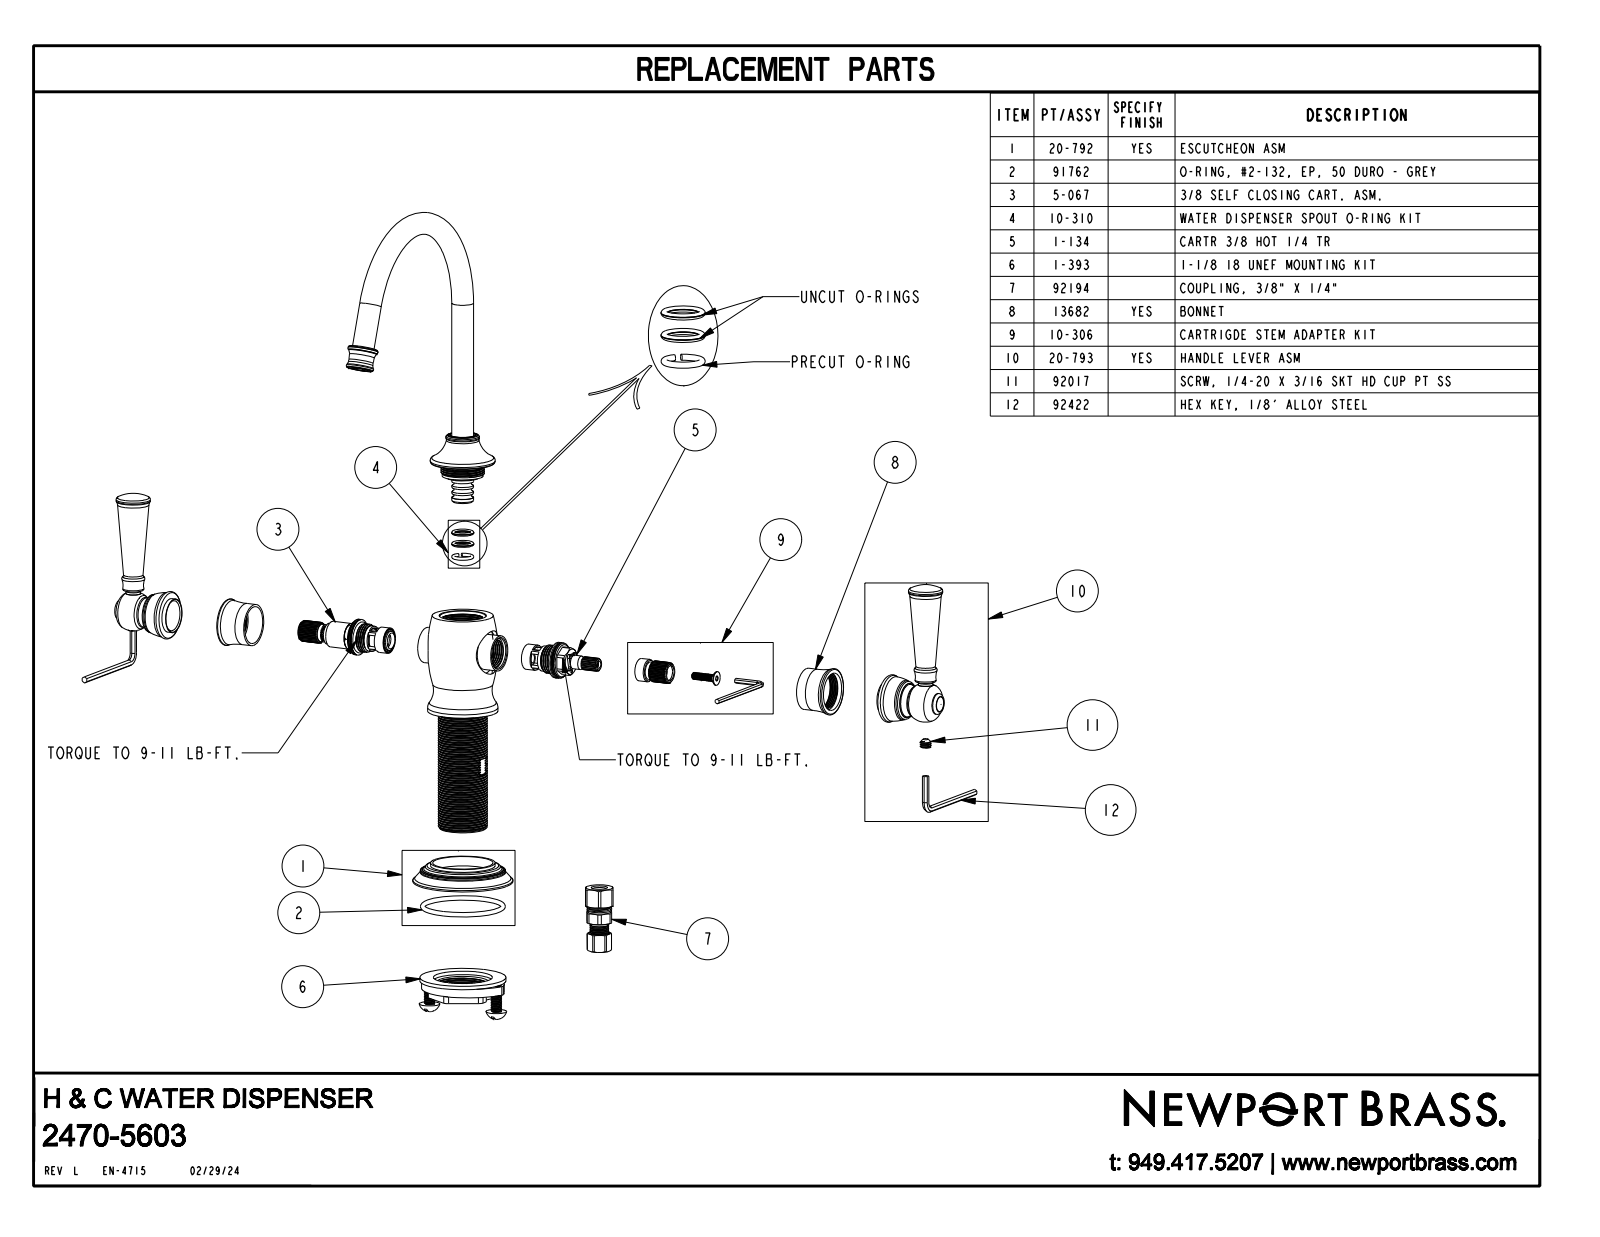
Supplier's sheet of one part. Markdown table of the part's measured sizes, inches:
| quantity | value |
| --- | --- |
| part name | 2470-5603 |
| STEP written by | CREO PARAMETRIC BY PTC INC, 2018400 (CONFIG_CONTROL_DESIGN) |
| units | inches |
| bodies | 1 solid, 243 faces (23 planar, 34 cylindrical, 186 other) |
| overall size | 9.456 × 6.18 × 5.353 |
| volume | 11.61 in³ |
| surface area | 62.91 in² |
| round holes (diameter × count) | 1 × 1 |
| round bosses / shafts (diameter × count) | 0.5 × 3, 0.785 × 2, 0.335 × 2, 0.33 × 2, 1.61 × 1, 0.95 × 1, 0.48 × 1 |
| main face-to-face distances | 2.615, 2.595, 0.02, 0.025, 2.57, 2.59, 0.68, 1.89, 3.266, 0.374 |
